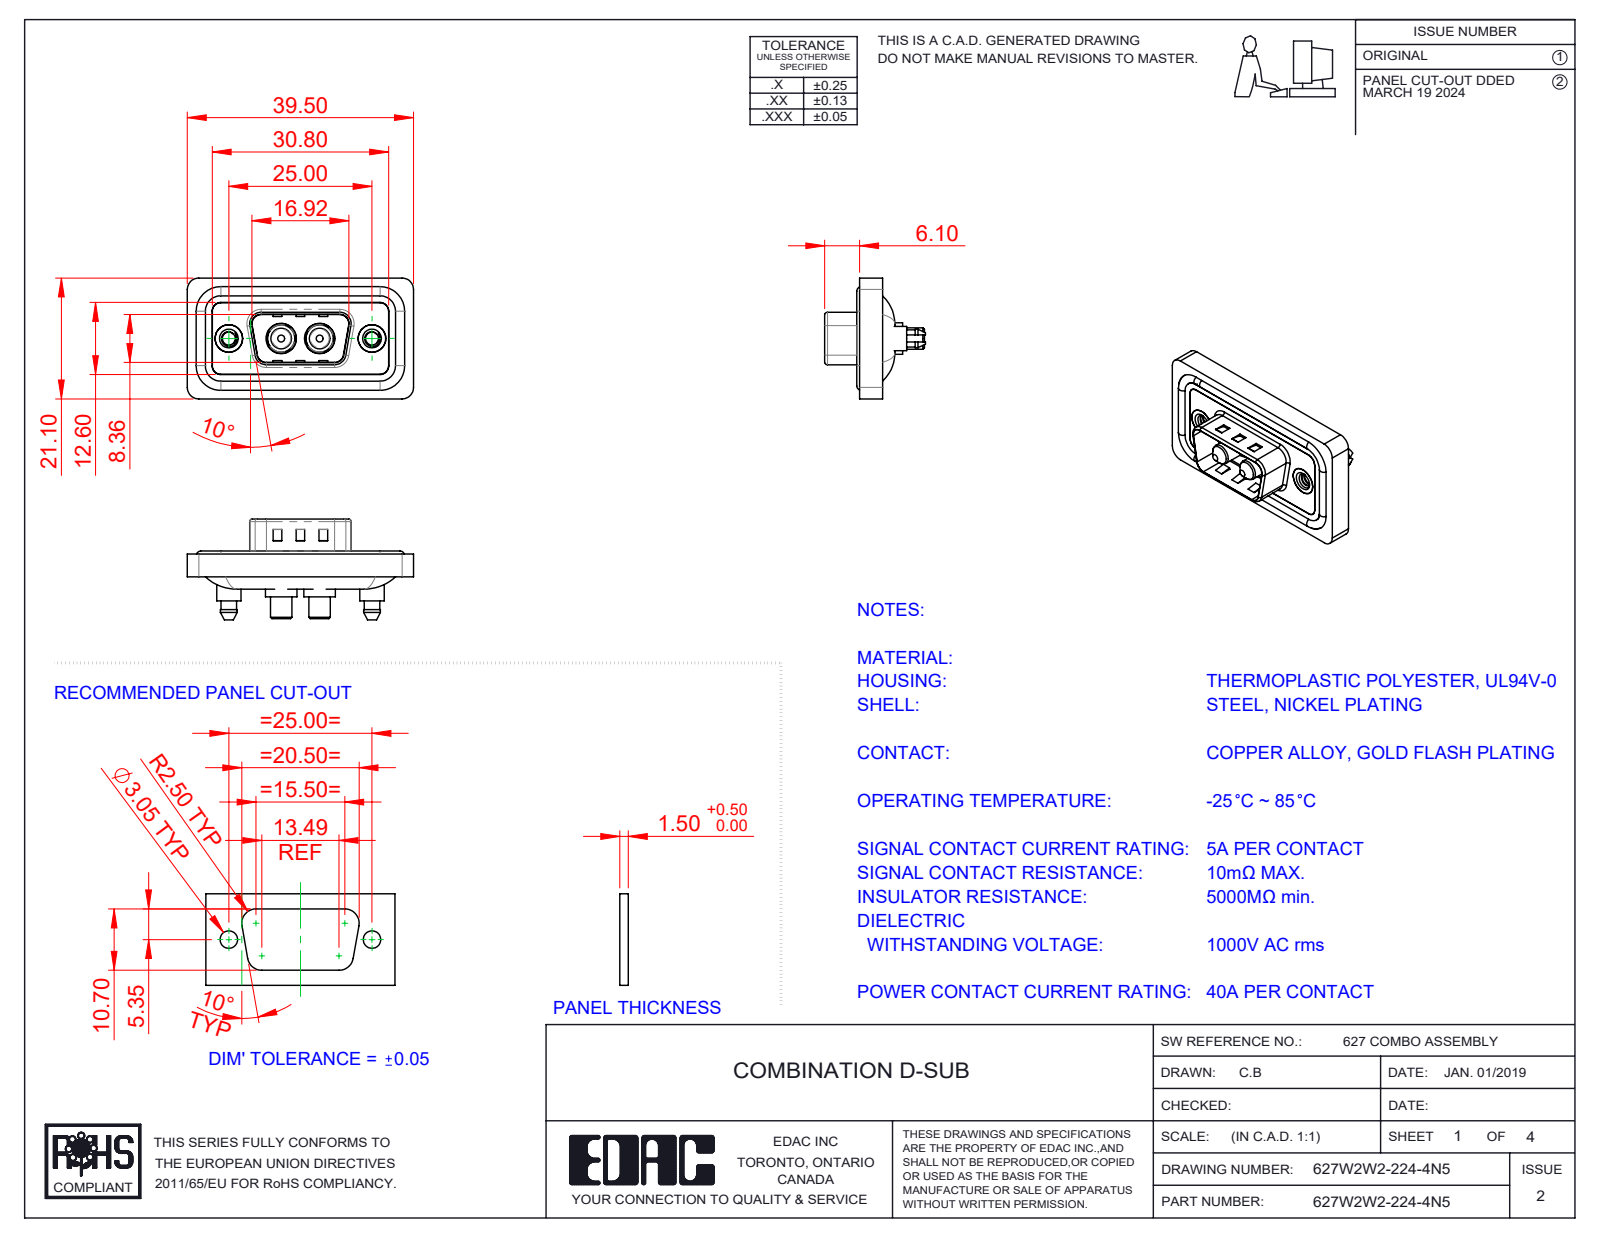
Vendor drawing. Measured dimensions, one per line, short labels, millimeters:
name: 627Combo Shell Rear_09 Contacts; Power Pin_40A S; 627W2W2-224-4N5; 627Combo Housing_2W2 (+3 more)
written by: SolidWorks 2023 (CONFIG_CONTROL_DESIGN)
unit: mm
bodies: 11 solids, 539 faces (181 planar, 250 cylindrical, 108 other)
size: 39.5 × 21.1 × 17.6
volume: 4 631 mm³; area: 7 339 mm²
holes: 2× ⌀2.26, 2× ⌀4, 2× ⌀4.8, 2× ⌀4.85, 2× ⌀5, 2× ⌀5.3
bosses: 4× ⌀1.6, 2× ⌀5.5, 2× ⌀5.4, 2× ⌀5.2, 2× ⌀4.9, 2× ⌀4.75, 2× ⌀4.25, 2× ⌀3.75
rounds: 24× R1.5, 18× R2, 10× R1.6, 8× R0.5, 4× R0.25, 4× R0.6, 4× R0.65, 4× R0.9
face distances: 0.4, 1.1, 2.9, 3.1, 0.5, 1.6, 1.5, 4, 0.7, 2.5
hole spacings: 9.14, 15.86, 6.72, 25
